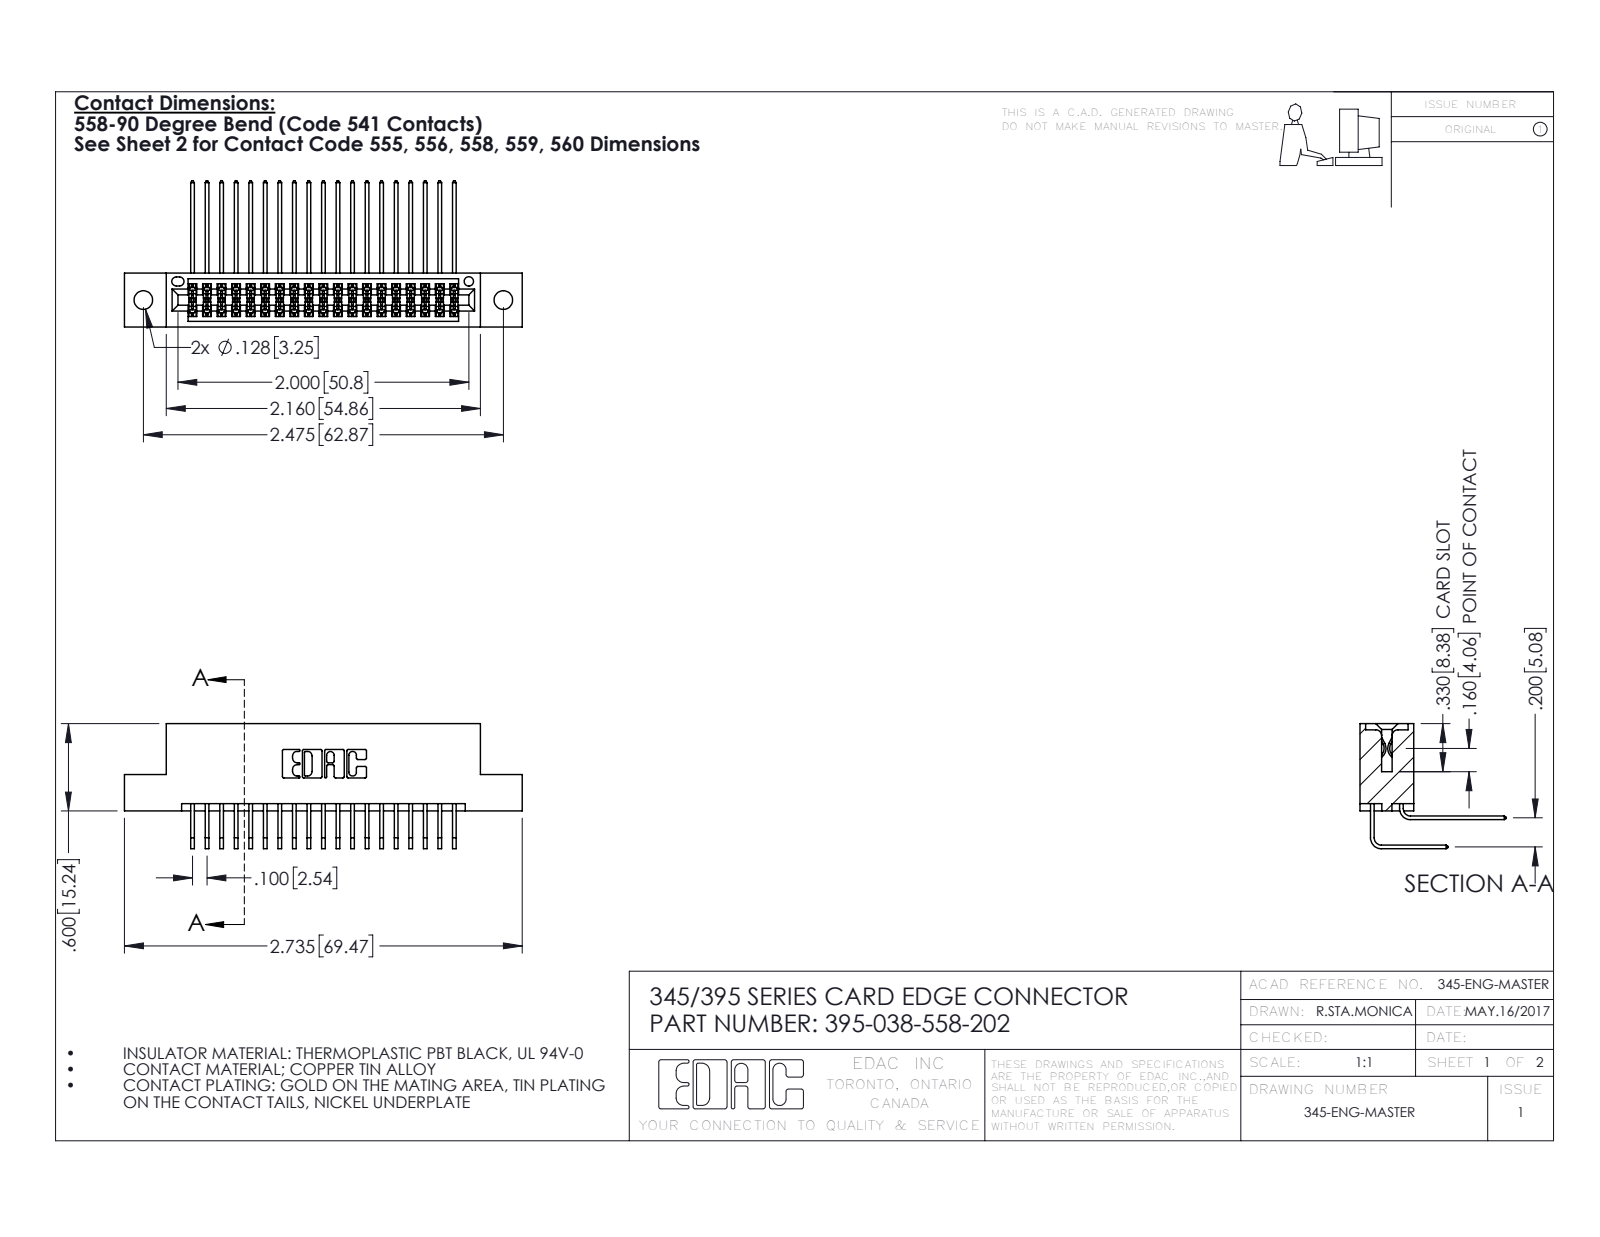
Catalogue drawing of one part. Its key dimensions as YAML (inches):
part_name: "345-292-001_558 559 Tail - 1; 345 Part_Flush Mounting Lugs - 0.128 Dia; 395-038-558-202; 345-292-001_558 Tail - 2"
step_written_by: "SolidWorks 2016 (CONFIG_CONTROL_DESIGN)"
units: inches
bodies: {solids: 39, faces: 2102, planar: 1410, cylindrical: 692, other: 0}
overall_size: [2.735, 1.005, 0.859]
volume: 0.41
surface_area: 15.88
round_holes:
  - {diameter: 0.128, count: 2}
  - {diameter: 0.064, count: 1}
partial_cylinders:
  - {radius: 0.006, count: 58}
  - {radius: 0.01, count: 22}
  - {radius: 0.007, count: 6}
  - {radius: 0.031, count: 6}
  - {radius: 0.026, count: 3}
  - {radius: 0.014, count: 2}
  - {radius: 0.019, count: 2}
  - {radius: 0.022, count: 2}
face_to_face_distances: [0.2, 0.072, 0.298, 0.37, 0.098, 0.272, 0.025, 0.225, 0.285, 0.025]
hole_center_spacings: [0.27, 2.241, 2.475]
